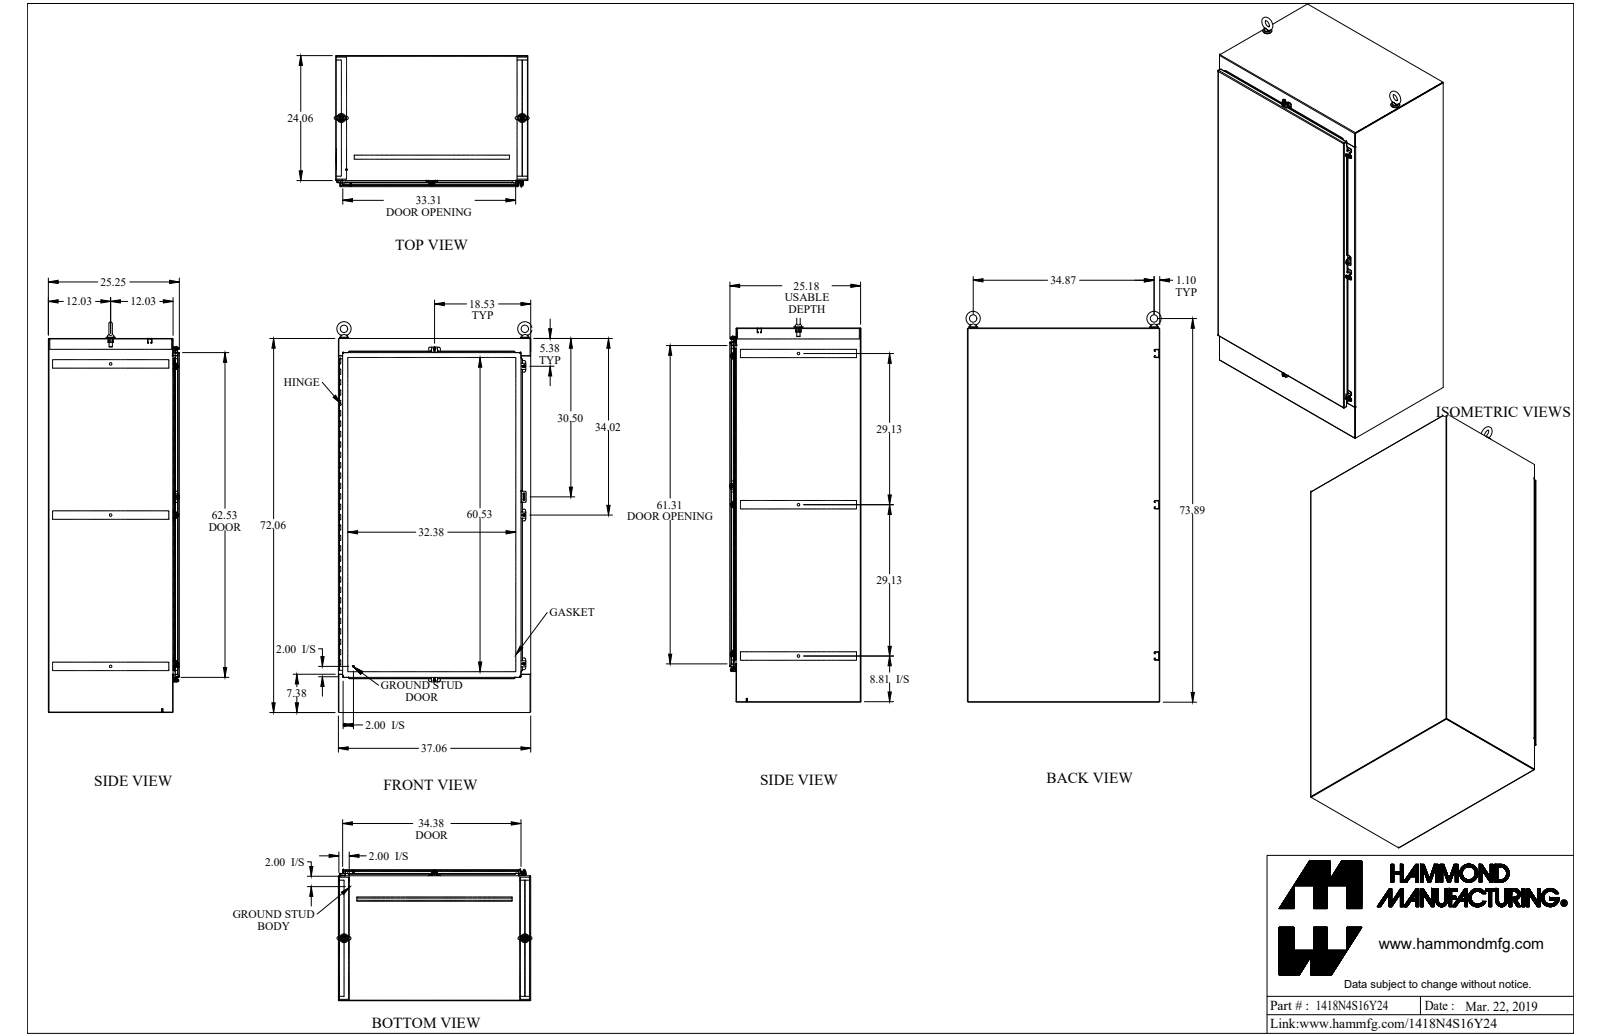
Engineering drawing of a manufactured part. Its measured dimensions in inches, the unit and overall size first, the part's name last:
Units: inches
Overall size (bounding box): 75.719 × 38.118 × 25.31
Round holes (diameter × count): ⌀0.304 ×10, ⌀0.213 ×5, ⌀0.375 ×5, ⌀0.265 ×3, ⌀0.5 ×3, ⌀0.265 ×2, ⌀0.527 ×2, ⌀0.68 ×2, ⌀0.75 ×2, ⌀0.11 ×1, ⌀0.125 ×1, ⌀0.625 ×1
Round bosses / shafts (diameter × count): ⌀0.5 ×5, ⌀0.39 ×5, ⌀0.244 ×5, ⌀1.75 ×2, ⌀1.5 ×2, ⌀1.25 ×2, ⌀0.738 ×2, ⌀0.313 ×2
Partial cylindrical surfaces — rounded edges, fillets, slot ends (radius × count): R0.043 ×60, R0.138 ×54, R0.048 ×43, R0.143 ×43, R0.25 ×26, R0.06 ×10, R0.141 ×10, R0.125 ×8
Main face-to-face distances: 0.095, 25.152, 36.965, 25.057, 25.247, 36.87, 71.965, 37.06, 1.187, 23.965
Hole centre spacings: 6, 12, 18, 24, 30, 36, 42, 29.13
Volume: 1 187 in³ · Surface area: 25 194 in²
Bodies: 54 solids, 1900 faces (940 planar, 844 cylindrical, 116 other)
Part name (STEP PRODUCT): 1418N4S16Y24_Default
STEP written by: SolidWorks 2019 (CONFIG_CONTROL_DESIGN)
